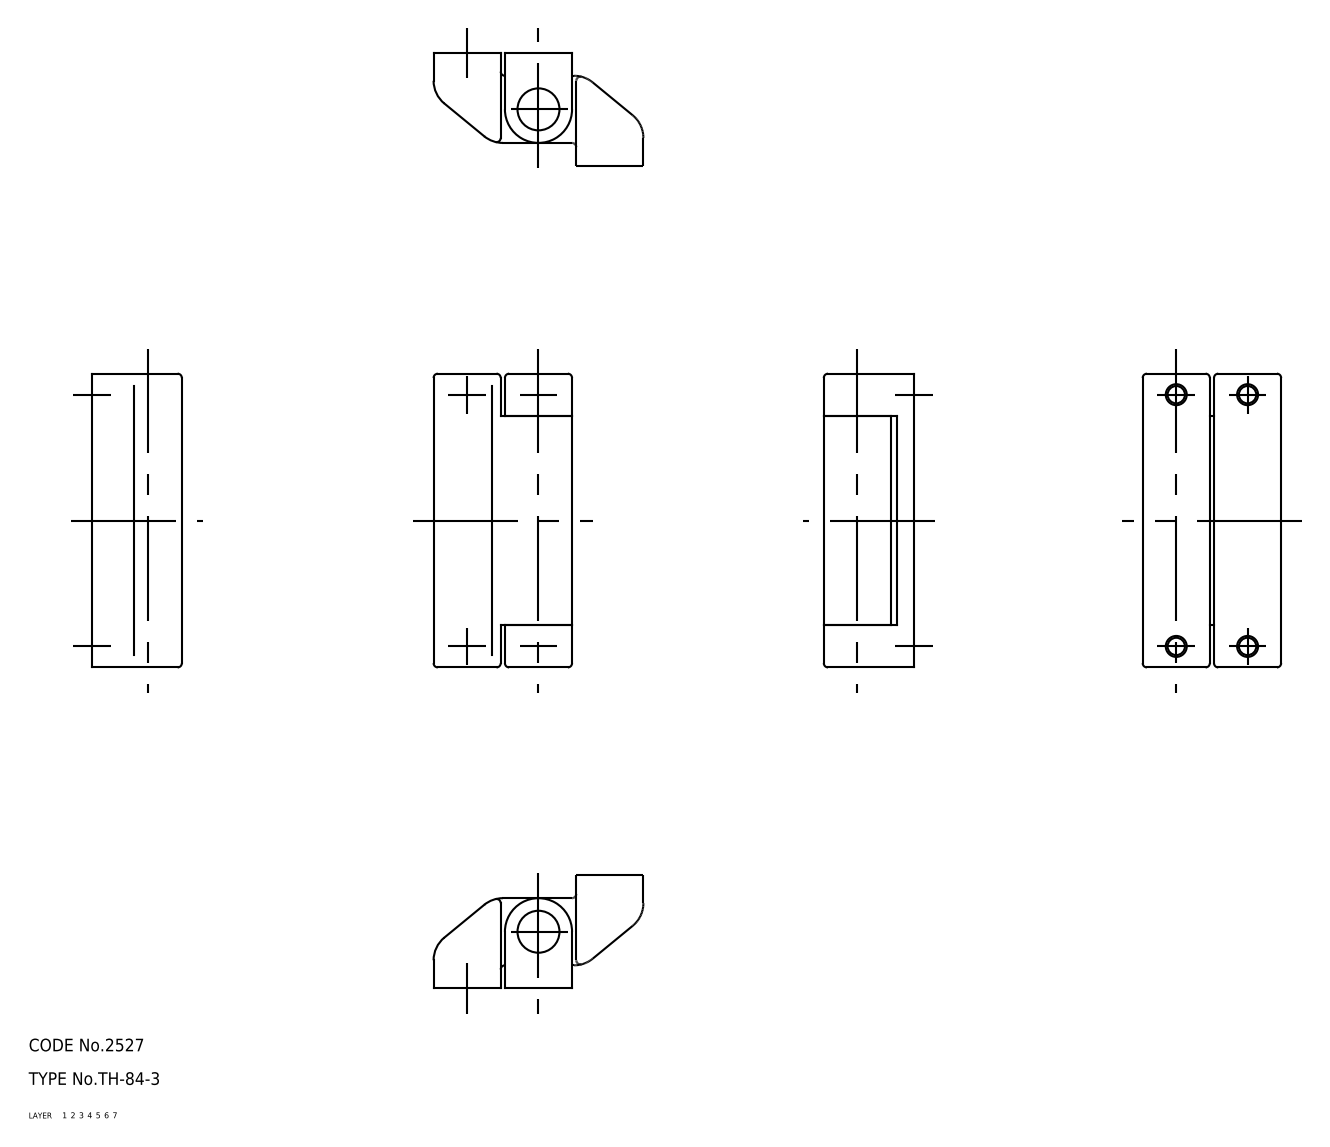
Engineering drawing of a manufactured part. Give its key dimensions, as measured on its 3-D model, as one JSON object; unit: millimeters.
{"part_name": "shaft; hinge piece_B; hinge piece_A; TH_84_3_17970_36", "step_written_by": "CADfix (AUTOMOTIVE_DESIGN)", "units": "millimeters", "bodies": {"solids": 3, "faces": 74, "planar": 0, "cylindrical": 0, "other": 74}, "overall_size": [70, 33, 21.5], "volume_mm3": 39298, "surface_area_mm2": 15963}
